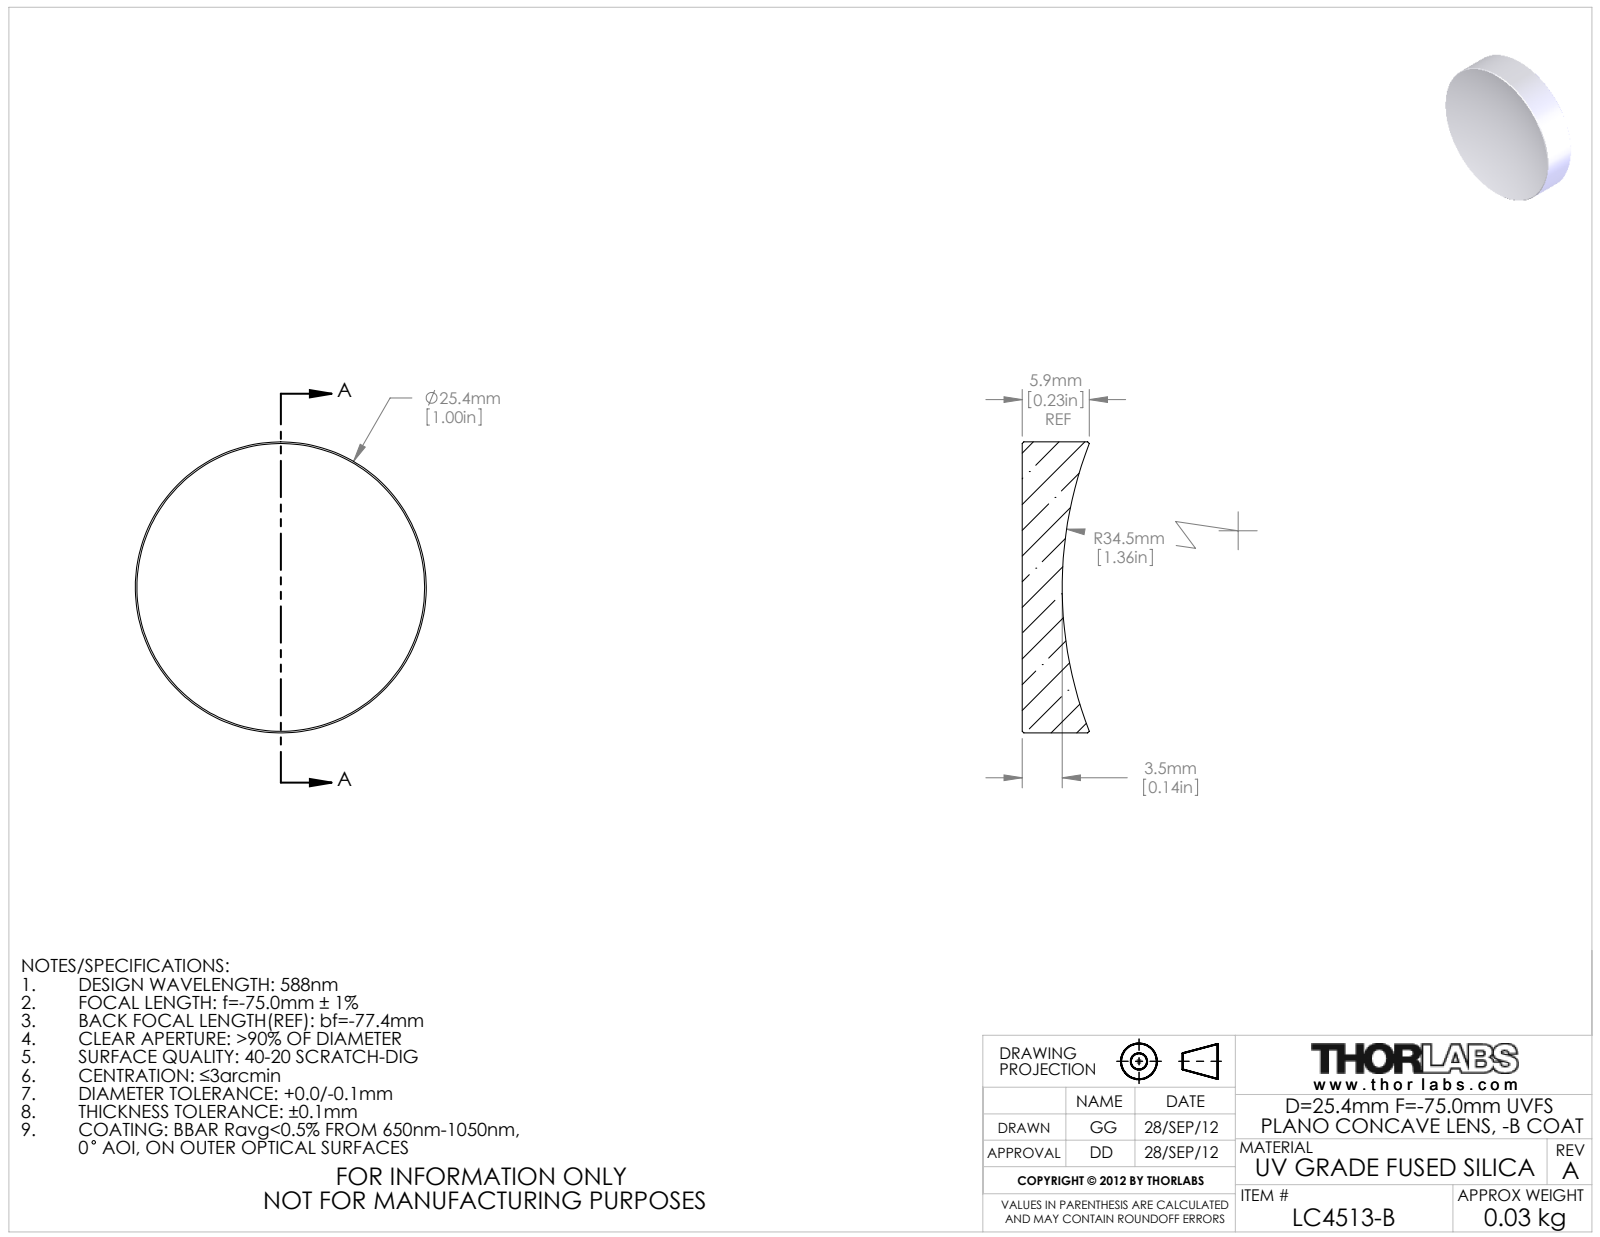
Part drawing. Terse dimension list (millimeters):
name: 25021-E0W
written by: SolidWorks 2011 (CONFIG_CONTROL_DESIGN)
unit: mm
bodies: 1 solid, 9 faces (1 planar, 2 cylindrical, 6 other)
size: 25.4 × 25.4 × 5.87
volume: 2 378 mm³; area: 1 486 mm²
bosses: 1× ⌀25.4
